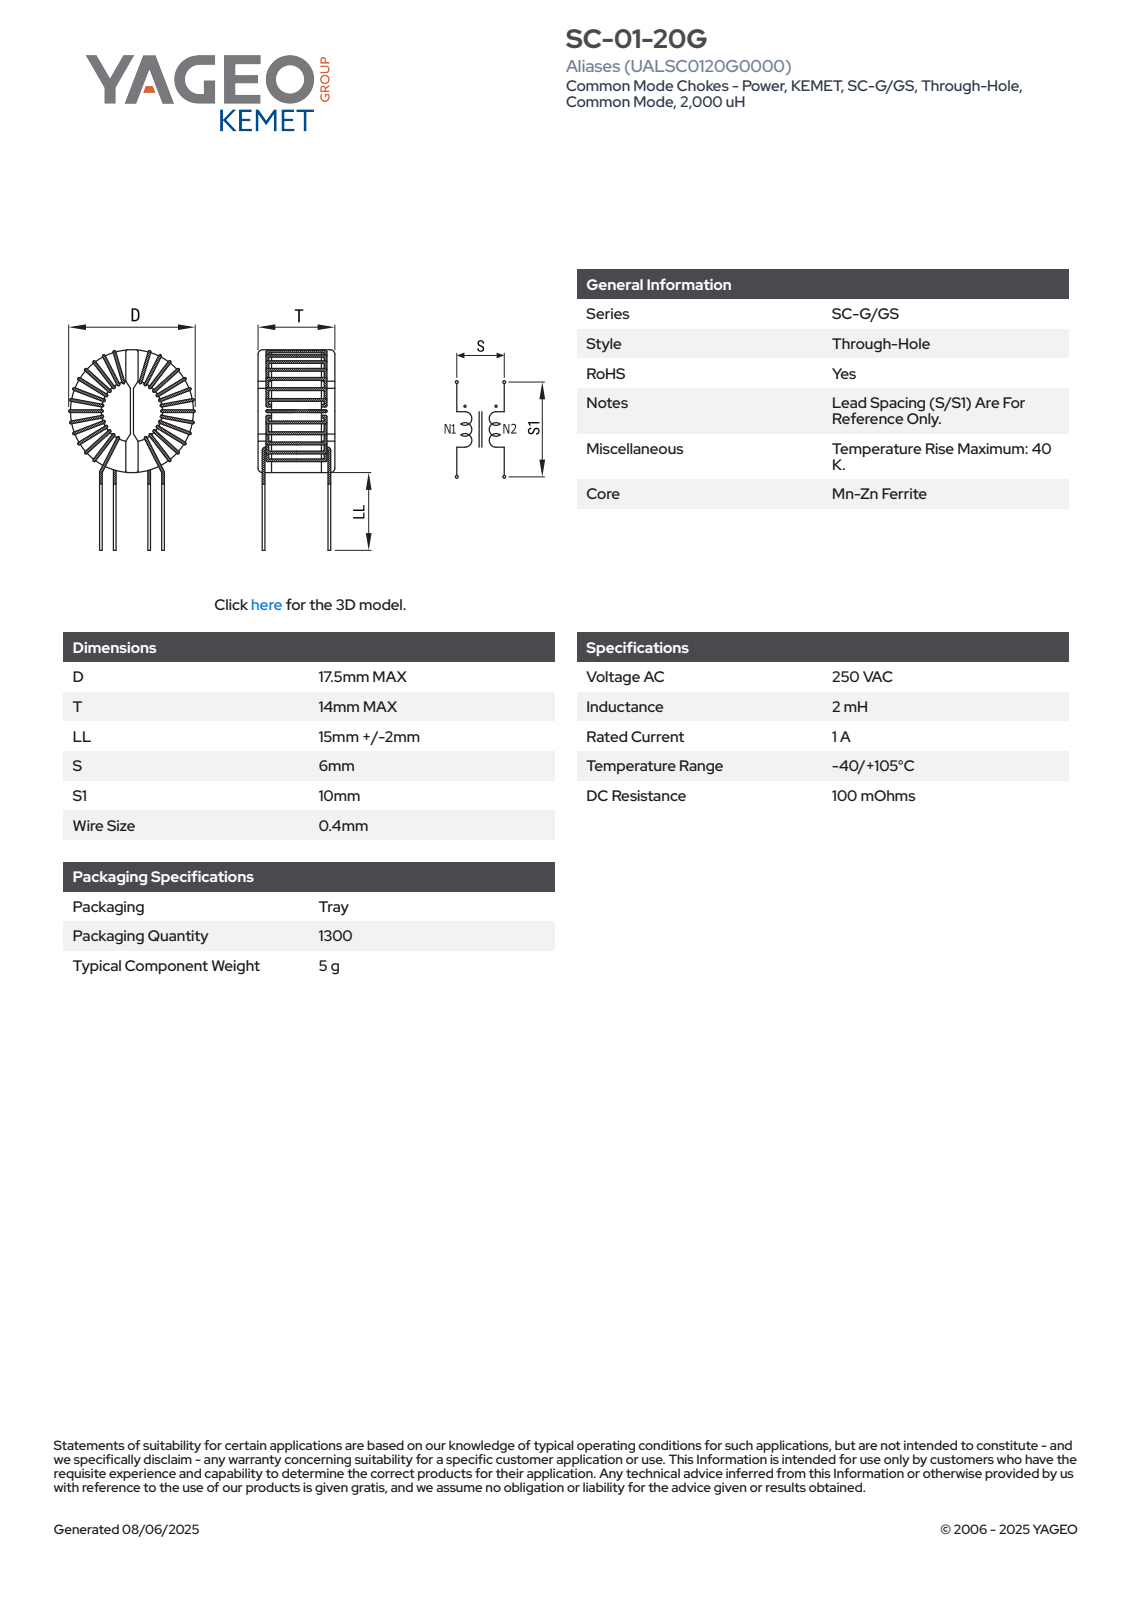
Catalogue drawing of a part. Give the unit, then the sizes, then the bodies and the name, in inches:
Units: inches
Overall size (bounding box): 1.196 × 0.689 × 0.551
Round bosses / shafts (diameter × count): ⌀0.016 ×8
Partial cylindrical surfaces — rounded edges, fillets, slot ends (radius × count): R0.008 ×16, R0.091 ×1, R0.126 ×1, R0.143 ×1, R0.144 ×1, R0.15 ×1, R0.25 ×1, R0.252 ×1
Main face-to-face distances: 0.047, 0.079, 0.327, 0.031, 0.126, 0.112, 0.439, 0.045, 0.081, 0.033
Volume: 0.109 in³ · Surface area: 2.651 in²
Bodies: 1 solid, 268 faces (121 planar, 65 cylindrical, 82 other)
Part name (STEP PRODUCT): SC-01-20G
STEP written by: SolidWorks 2018 (AUTOMOTIVE_DESIGN)
